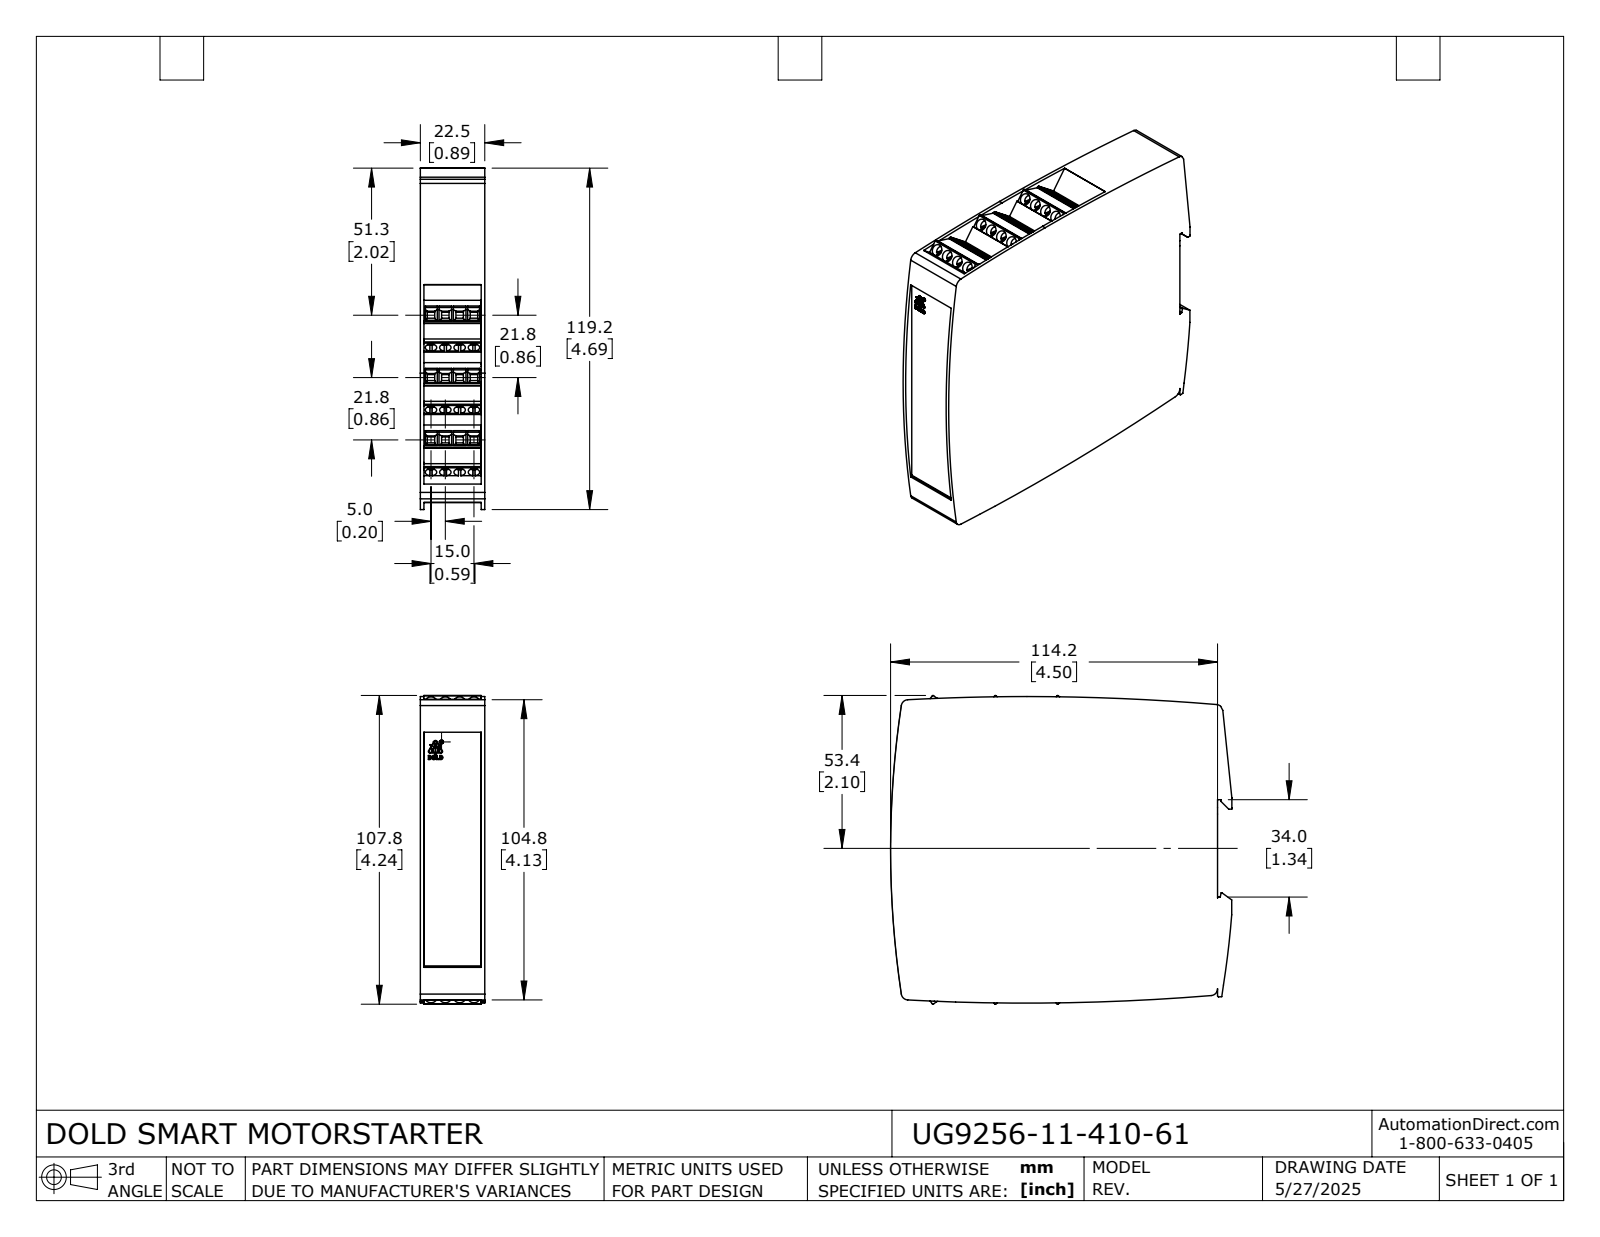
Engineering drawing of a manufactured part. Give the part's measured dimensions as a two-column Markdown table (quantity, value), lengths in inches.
| quantity | value |
| --- | --- |
| part name | UG9256-11-410-61 |
| STEP written by | SolidWorks 2024 (AUTOMOTIVE_DESIGN) |
| units | inches |
| bodies | 1 solid, 1036 faces (813 planar, 222 cylindrical, 1 other) |
| overall size | 4.693 × 4.243 × 0.886 |
| volume | 15.85 in³ |
| surface area | 64.72 in² |
| round holes (diameter × count) | 0.157 × 24, 0.053 × 1 |
| round bosses / shafts (diameter × count) | 0.15 × 24, 0.049 × 1 |
| partial cylindrical surfaces (radius × count) | 0.012 × 15, 0.02 × 14, 0.004 × 12, 0.094 × 7, 0.005 × 6, 0.004 × 4, 31.496 × 4, 0.021 × 3 |
| main face-to-face distances | 0.886, 0.049, 0.837, 0.675, 4.379, 0.051, 0.835, 1.35, 0.528, 0.785 |
| hole center spacings | 0.563, 0.197, 0.528, 0.658, 0.394, 1.073, 0.792, 1.055 |
